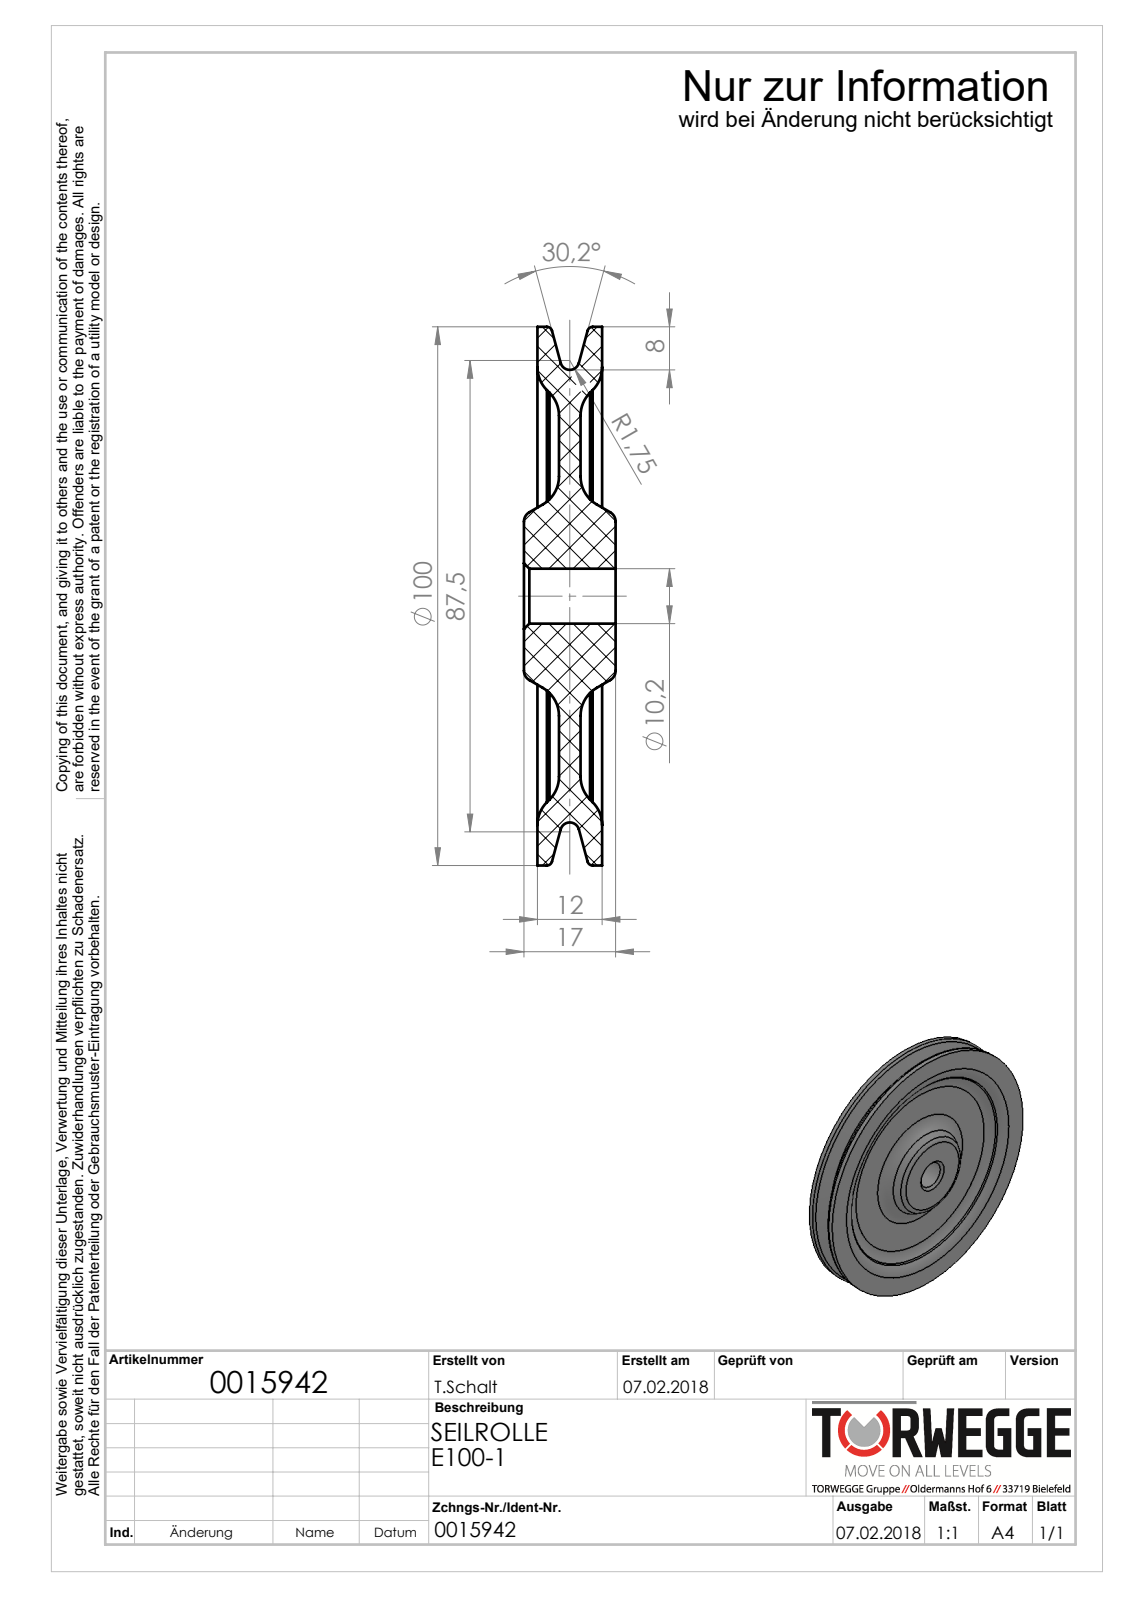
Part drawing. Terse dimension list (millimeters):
name: 0015942_E100-1
written by: SolidWorks 2018 (AUTOMOTIVE_DESIGN)
unit: mm
bodies: 1 solid, 27 faces (6 planar, 3 cylindrical, 18 other)
size: 100 × 100 × 17
volume: 57 355 mm³; area: 23 949 mm²
holes: 1× ⌀10.2
bosses: 1× ⌀100
face distances: 4, 8, 12, 2.5, 6.5, 10.5, 14.5, 17
